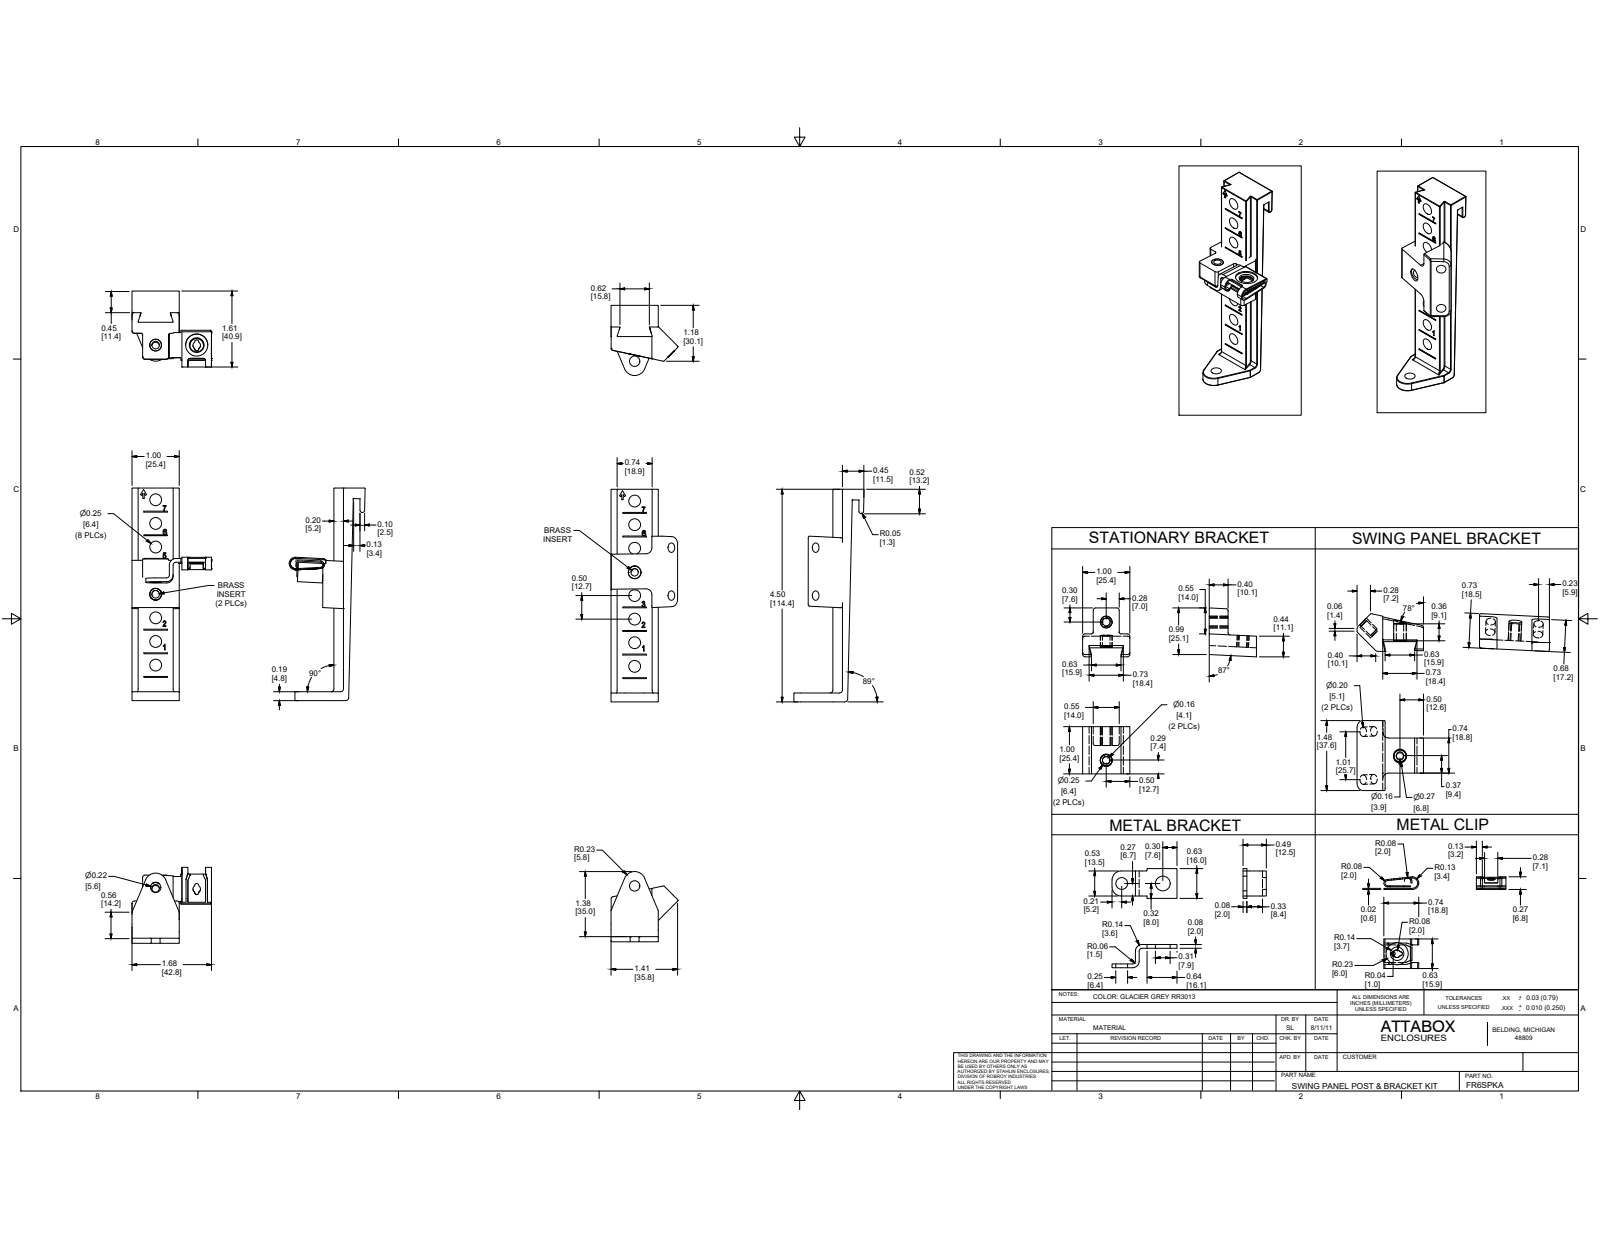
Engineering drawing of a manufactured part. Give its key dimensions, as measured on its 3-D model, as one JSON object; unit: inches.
{"part_name": "FR6SPKA", "step_written_by": "SolidWorks 2019 (AUTOMOTIVE_DESIGN)", "units": "inches", "bodies": {"solids": 32, "faces": 1564, "planar": 740, "cylindrical": 402, "other": 422}, "overall_size": [10.622, 8.622, 4.728], "volume_in3": 8.407, "surface_area_in2": 115.5, "round_holes": [[0.25, 34], [0.156, 6], [0.253, 6], [0.217, 4], [0.22, 4], [0.312, 3], [0.35, 2]], "round_bosses_or_shafts": [[0.19, 10], [0.373, 6], [0.246, 6], [0.433, 4], [0.315, 4]], "partial_cylinders_radius": [[0.01, 206], [0.06, 44], [0.063, 12], [0.025, 8], [0.13, 8], [0.062, 6], [0.049, 4], [0.19, 4]], "face_to_face_distances": [11.295, 6.855, 4.441, 5.44, 5.855, 1.415, 1, 4.502, 0.203, 4.643], "hole_center_spacings": [1.5, 0.5, 1, 1.732, 2.061, 2, 1.414, 2.45]}
